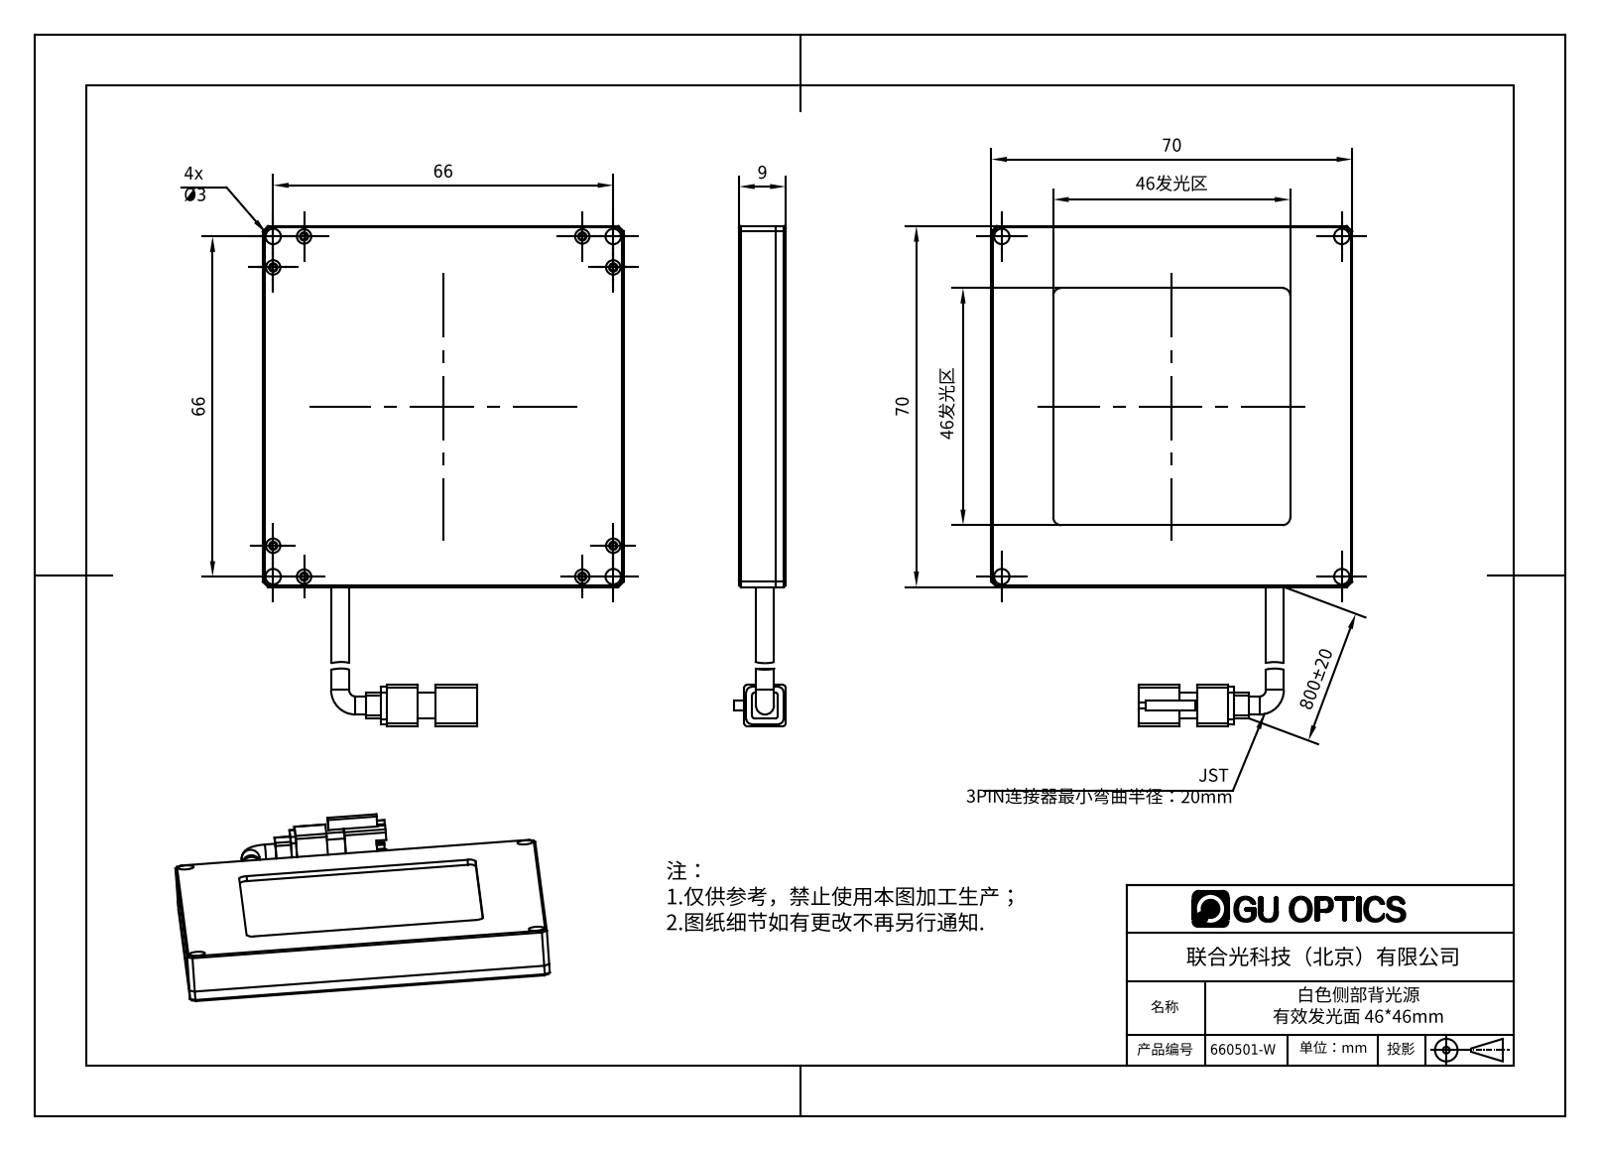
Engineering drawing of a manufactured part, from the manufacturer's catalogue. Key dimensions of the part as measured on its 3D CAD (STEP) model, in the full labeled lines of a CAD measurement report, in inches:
Part name (STEP PRODUCT): 660501-W
STEP written by: SolidWorks 2016 (AUTOMOTIVE_DESIGN)
Units: inches
Bodies: 6 solids, 436 faces (245 planar, 114 cylindrical, 77 other)
Overall size (bounding box): 3.819 × 2.756 × 0.394
Volume: 2.435 in³ · Surface area: 46.56 in²
Round holes (diameter × count): ⌀0.063 ×10, ⌀0.049 ×8, ⌀0.11 ×8, ⌀0.118 ×4
Round bosses / shafts (diameter × count): ⌀0.138 ×2
Partial cylindrical surfaces — rounded edges, fillets, slot ends (radius × count): R0.02 ×8, R0.079 ×6, R0.039 ×4, R0.059 ×4
Main face-to-face distances: 0.236, 0.079, 0.315, 0.039, 0.276, 0.354, 0.157, 2.598, 2.52, 2.362
Hole centre spacings: 2.598, 2.374, 2.609, 3.512, 0.236, 2.362, 3.357, 0.334
